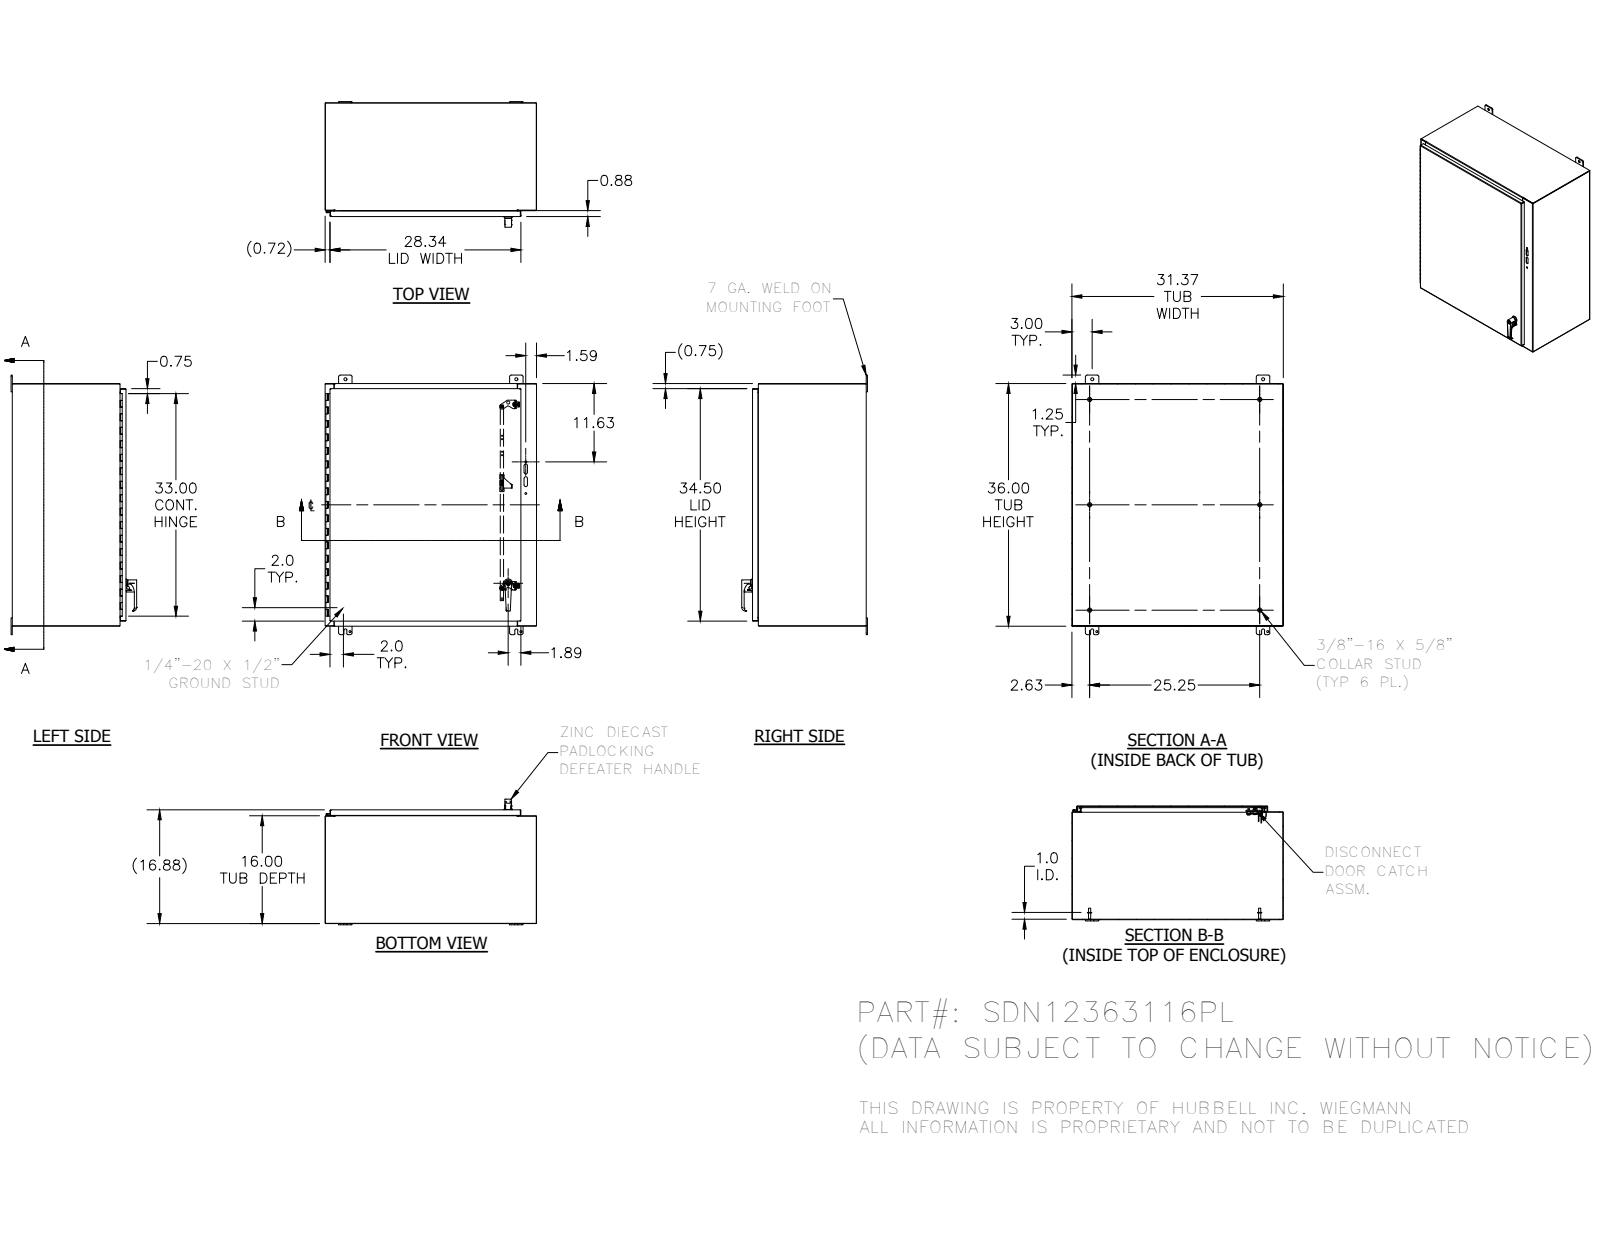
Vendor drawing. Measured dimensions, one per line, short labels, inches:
name: SDN12363116PL; SDN12363116PLBLR; 3889; 34840 (+8 more)
written by: Autodesk Inventor 2012 (AUTOMOTIVE_DESIGN)
unit: in
bodies: 53 solids, 1590 faces (848 planar, 523 cylindrical, 219 other)
size: 38.5 × 31.375 × 18.649
volume: 359.7 in³; area: 9 657 in²
holes: 6× ⌀0.145, 4× ⌀0.313, 4× ⌀0.438, 3× ⌀0.32, 2× ⌀0.156, 2× ⌀0.196, 2× ⌀0.211, 2× ⌀0.22, 2× ⌀0.281, 2× ⌀0.313, 2× ⌀0.45, 1× ⌀0.102
bosses: 7× ⌀0.625, 7× ⌀0.33, 4× ⌀0.437, 4× ⌀0.3, 4× ⌀0.25, 4× ⌀0.225, 4× ⌀0.19, 2× ⌀0.75
rounds: 38× R0.02, 30× R0.012, 22× R0.25, 18× R0.031, 18× R0.105, 16× R0.025, 15× R0.125, 6× R0.094
face distances: 0.074, 16.801, 31.301, 35.926, 16.727, 16.875, 31.227, 31.375, 35.852, 36
hole spacings: 1.593, 25.375, 36, 44.044, 0.5, 26.9, 2.375, 4.38
